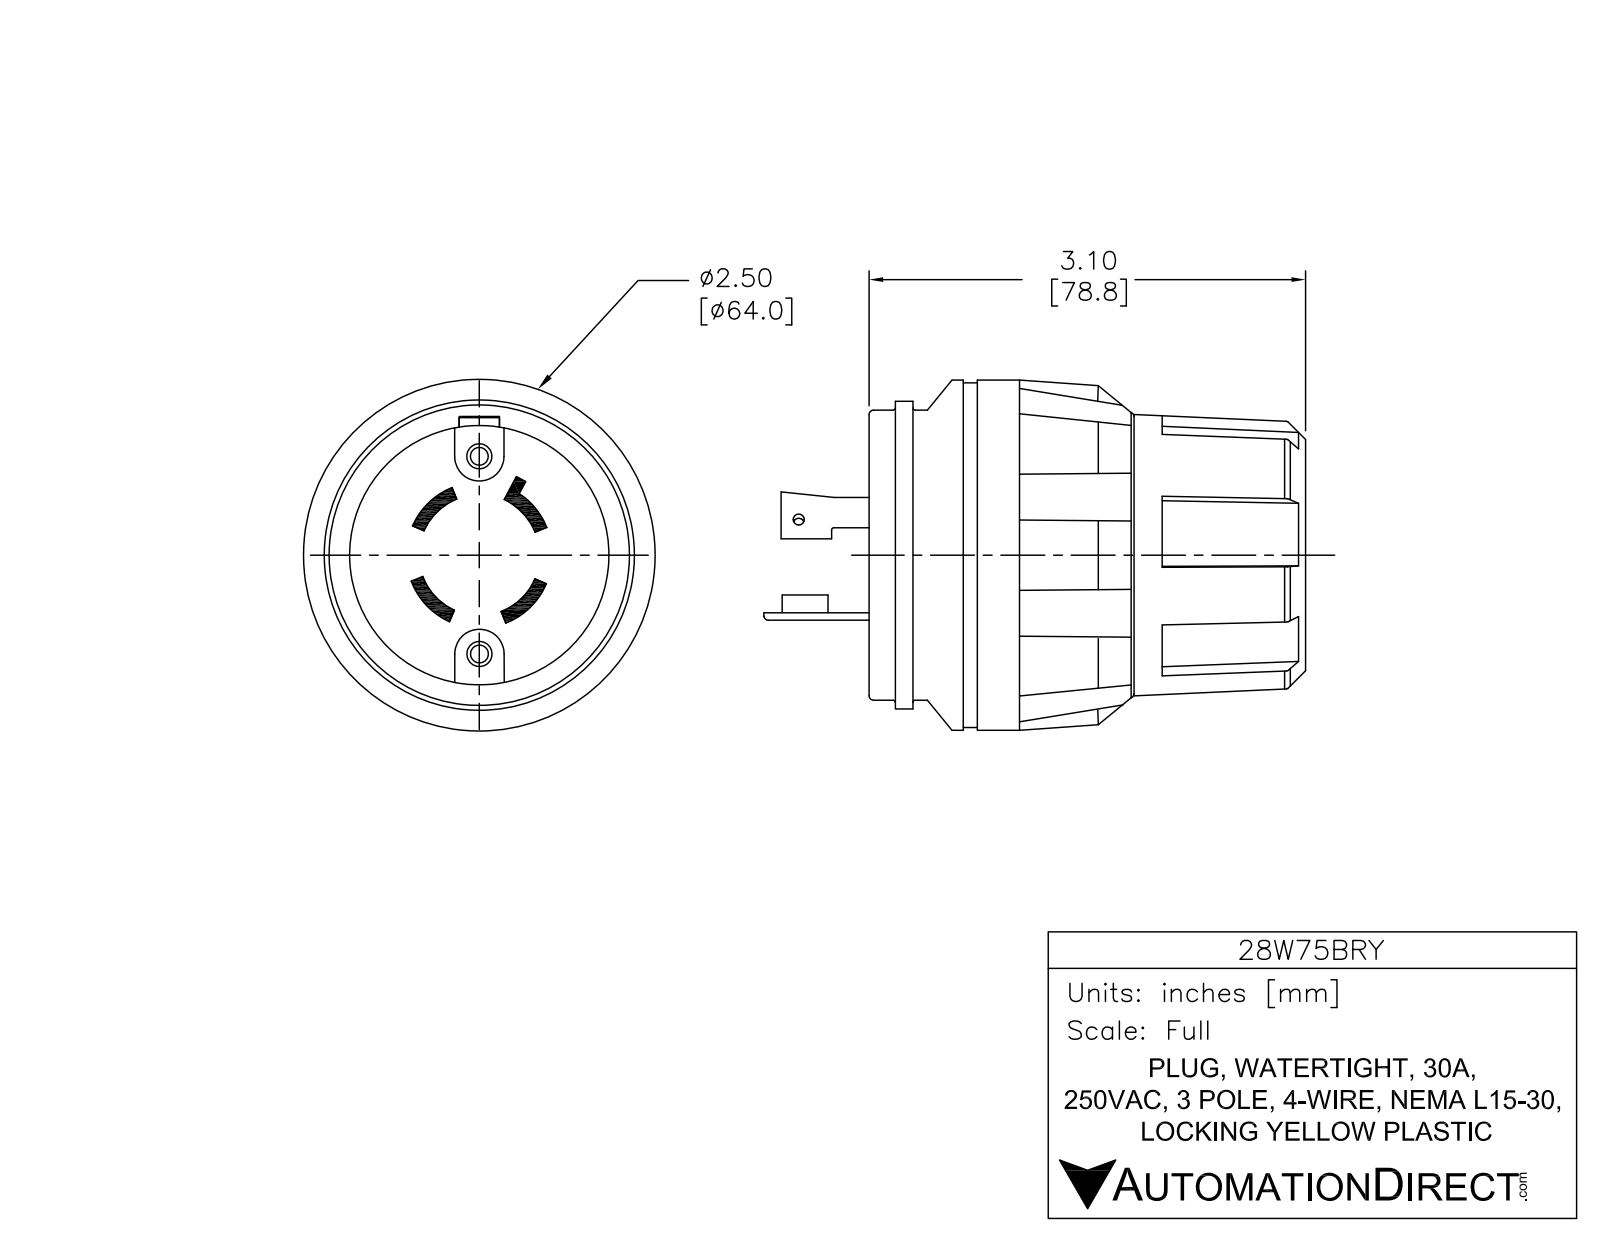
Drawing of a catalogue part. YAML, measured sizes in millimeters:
part_name: "28W75BRY"
step_written_by: "SolidWorks 2013 (AUTOMOTIVE_DESIGN)"
units: millimeters
bodies: {solids: 1, faces: 209, planar: 81, cylindrical: 56, other: 72}
overall_size: [105.3, 58, 58]
volume: 163200
surface_area: 25430
round_holes:
  - {diameter: 2.8, count: 2}
  - {diameter: 24.9, count: 1}
  - {diameter: 41.1, count: 1}
  - {diameter: 45.5, count: 1}
round_bosses_or_shafts:
  - {diameter: 6.1, count: 2}
  - {diameter: 58, count: 1}
  - {diameter: 56.5, count: 1}
  - {diameter: 52.7, count: 1}
  - {diameter: 36.1, count: 1}
partial_cylinders:
  - {radius: 0.8, count: 11}
  - {radius: 3.6, count: 2}
  - {radius: 1.5, count: 1}
  - {radius: 10.5, count: 1}
  - {radius: 12.1, count: 1}
face_to_face_distances: [51.7, 48.7, 3, 82.5, 33.8, 30.7, 0.3, 49, 52.1, 82.8]
